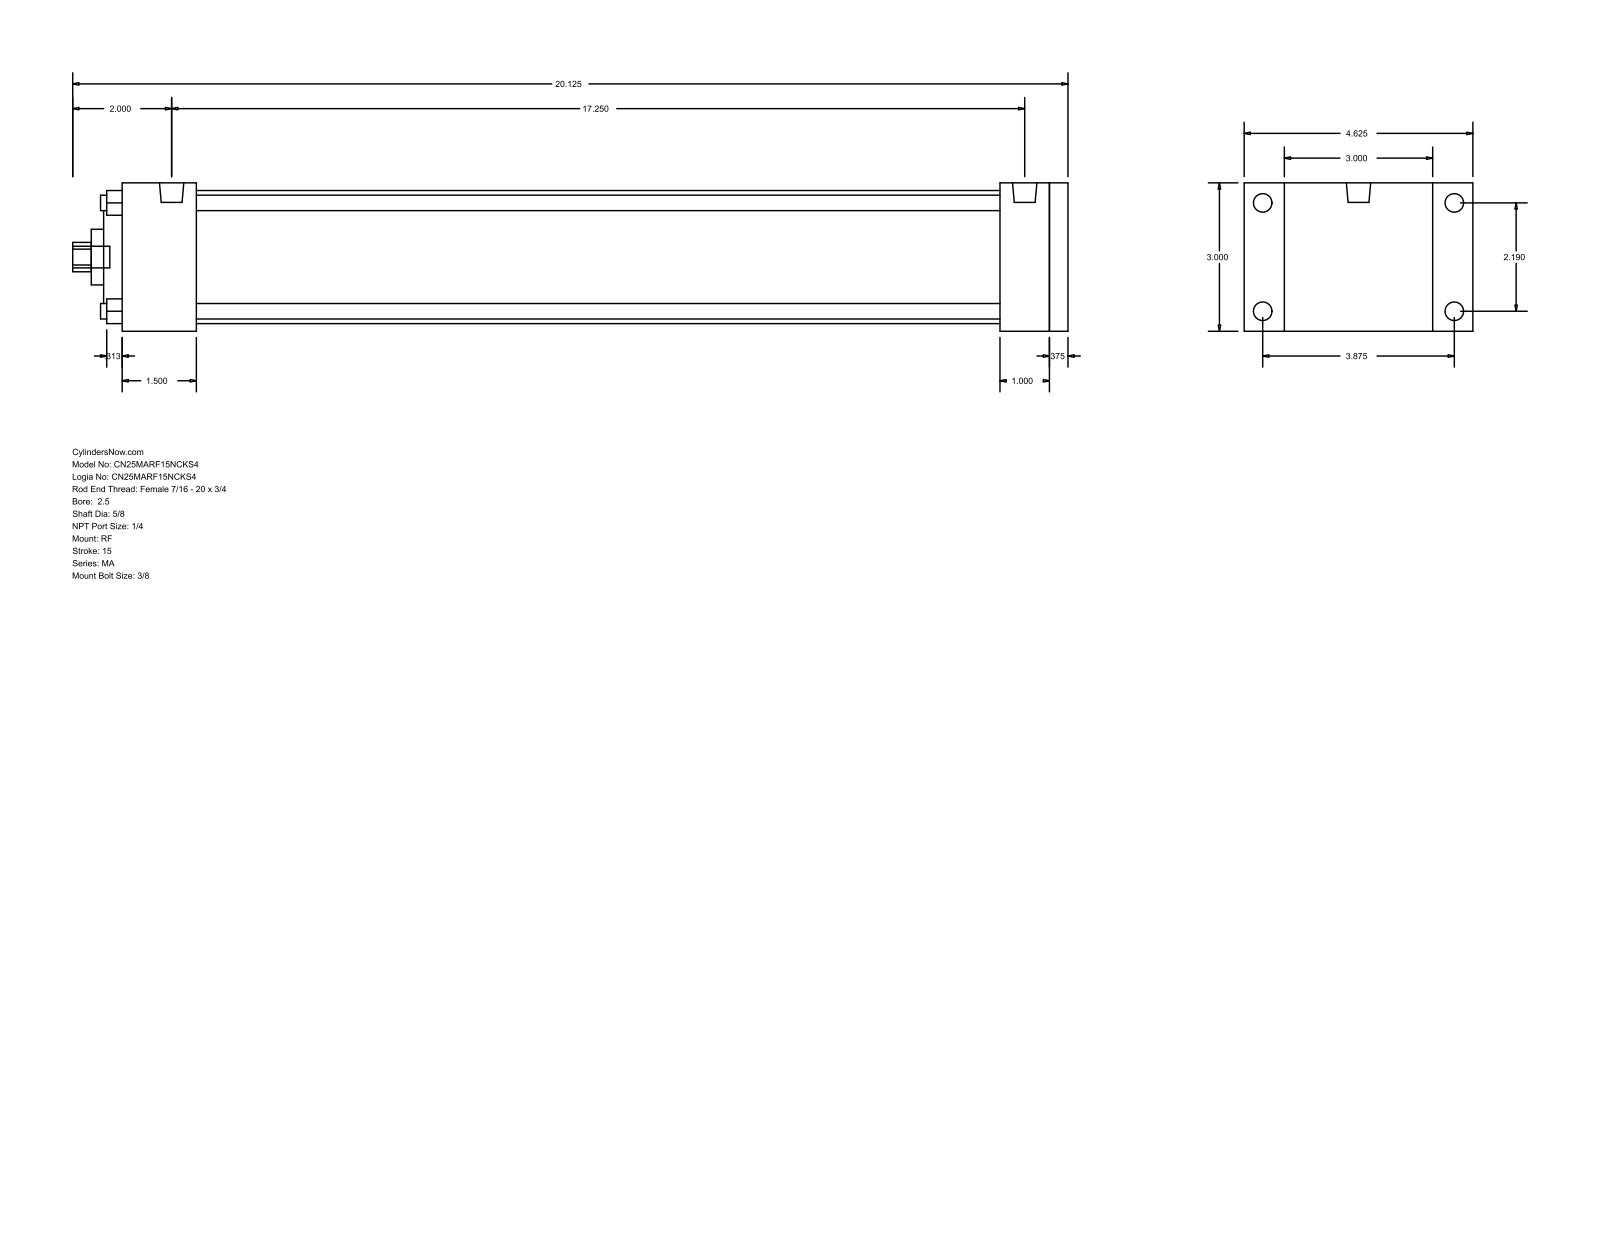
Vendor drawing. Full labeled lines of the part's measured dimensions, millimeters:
Part name (STEP PRODUCT): MA_RF__0250_0.625
STEP written by: GSSL Pune (CONFIG_CONTROL_DESIGN)
Units: millimetres
Bodies: 0 solids, 94 faces (65 planar, 29 cylindrical, 0 other)
Overall size (bounding box): 511.18 × 117.47 × 76.2
Round holes (diameter × count): ⌀7.94 ×4, ⌀15.88 ×1, ⌀28.57 ×1, ⌀50.8 ×1, ⌀68.33 ×1
Round bosses / shafts (diameter × count): ⌀9.53 ×4, ⌀7.94 ×4, ⌀12.49 ×2, ⌀11.11 ×1
Partial cylindrical surfaces — rounded edges, fillets, slot ends (radius × count): R7.54 ×1
Main face-to-face distances: 76.2, 485.78, 9.53, 476.25, 25.4, 38.1, 450.85, 412.75, 438.15, 447.68
Hole centre spacings: 39.33, 55.62, 78.66
